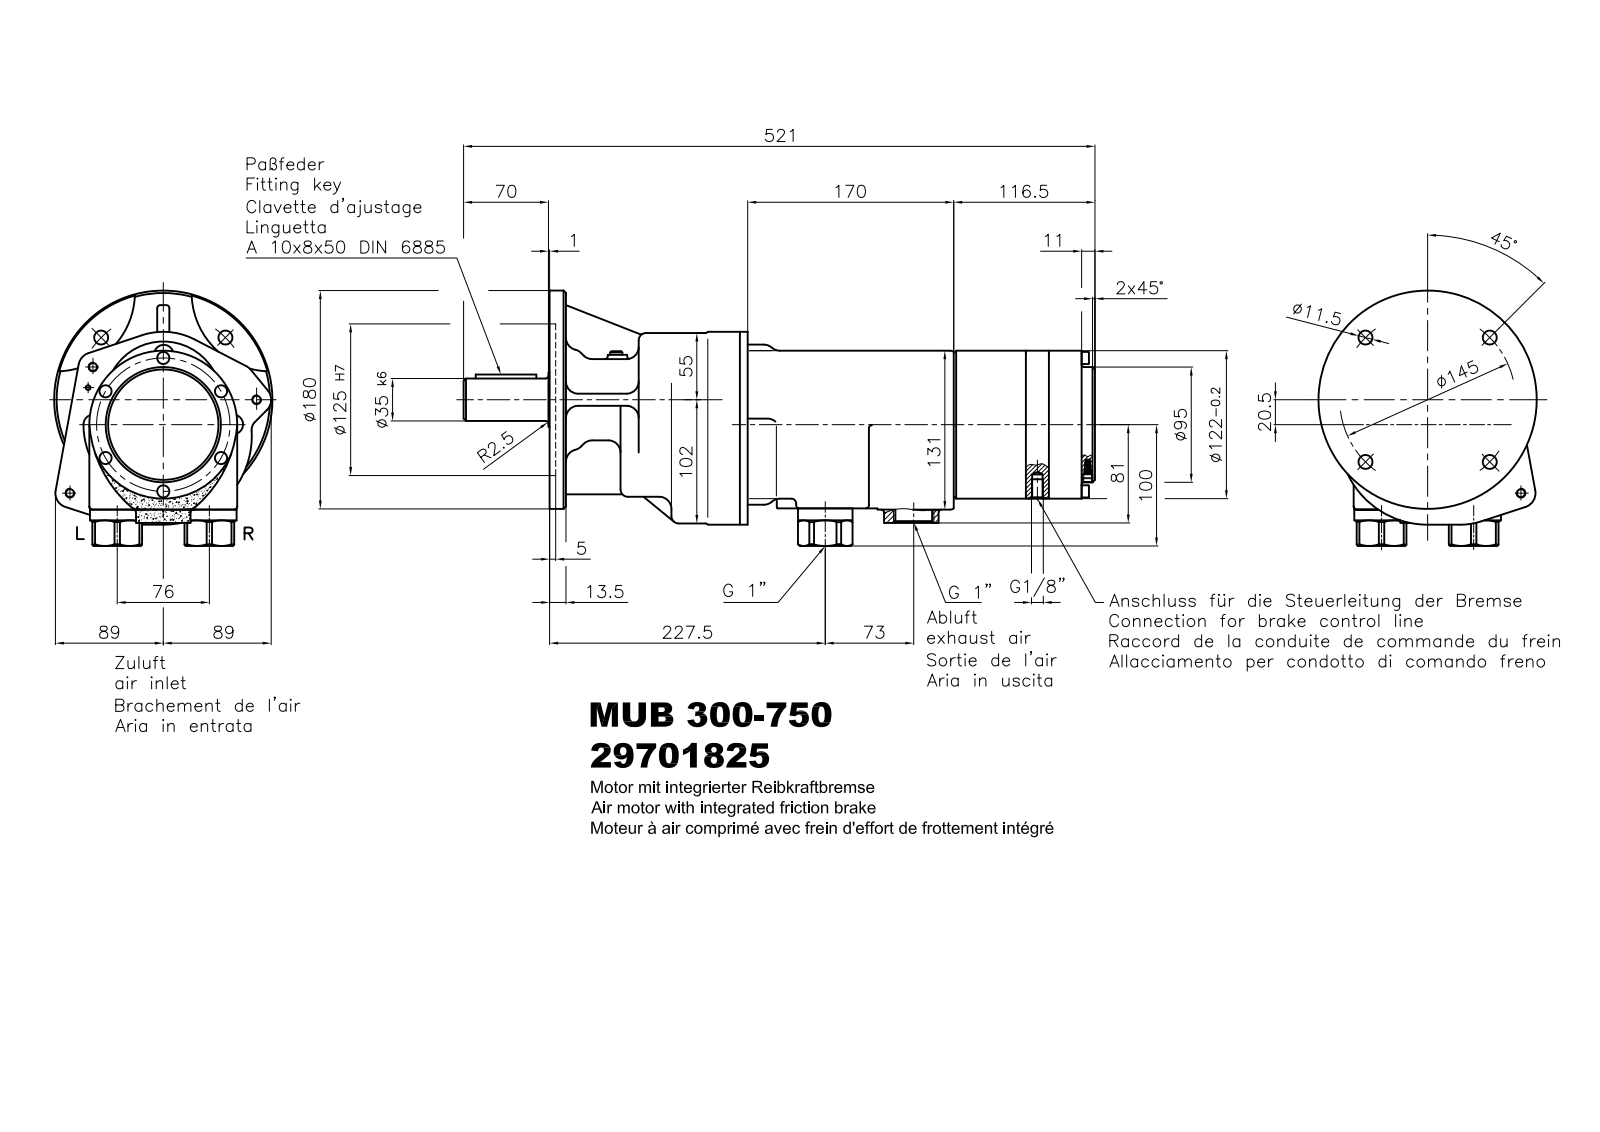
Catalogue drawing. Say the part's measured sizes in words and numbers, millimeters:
The part is named "MUB 300-500_29701835". Its 3-D file was written by "Autodesk Inventor 2008 (AUTOMOTIVE_DESIGN)". It is 1 solid with 677 faces: 213 planar, 230 cylindrical and 234 other. Overall it measures 521 by 193 by 180 millimeters. Its volume is 5 888 000 cubic millimeters and its surface area 313 590 square millimeters. Round holes: 4 of diameter 11.5, 3 of diameter 2.5, 3 of diameter 8.5, 3 of diameter 9.5, 2 of diameter 3, 2 of diameter 4.92, 2 of diameter 4.92, 2 of diameter 6.65, 2 of diameter 24.12, 2 of diameter 32, 1 of diameter 2.8, 1 of diameter 4.2. Round bosses or shafts: 7 of diameter 10, 3 of diameter 14.8, 3 of diameter 13, 3 of diameter 8, 2 of diameter 45, 1 of diameter 180, 1 of diameter 122, 1 of diameter 114. Partial cylindrical surfaces (rounded edges, fillets, slot ends): 31 of radius 4, 28 of radius 2.5, 13 of radius 6, 6 of radius 1, 6 of radius 1.5, 6 of radius 8, 6 of radius 11, 5 of radius 5. The main face-to-face distances are 5, 158.65, 163.65, 1, 150.15, 8.5, 13.5, 10, 7.5, 12.5. The hole center spacings are 30, 72.51, 81.71, 102.54, 76, 57.38, 60, 82.3.
